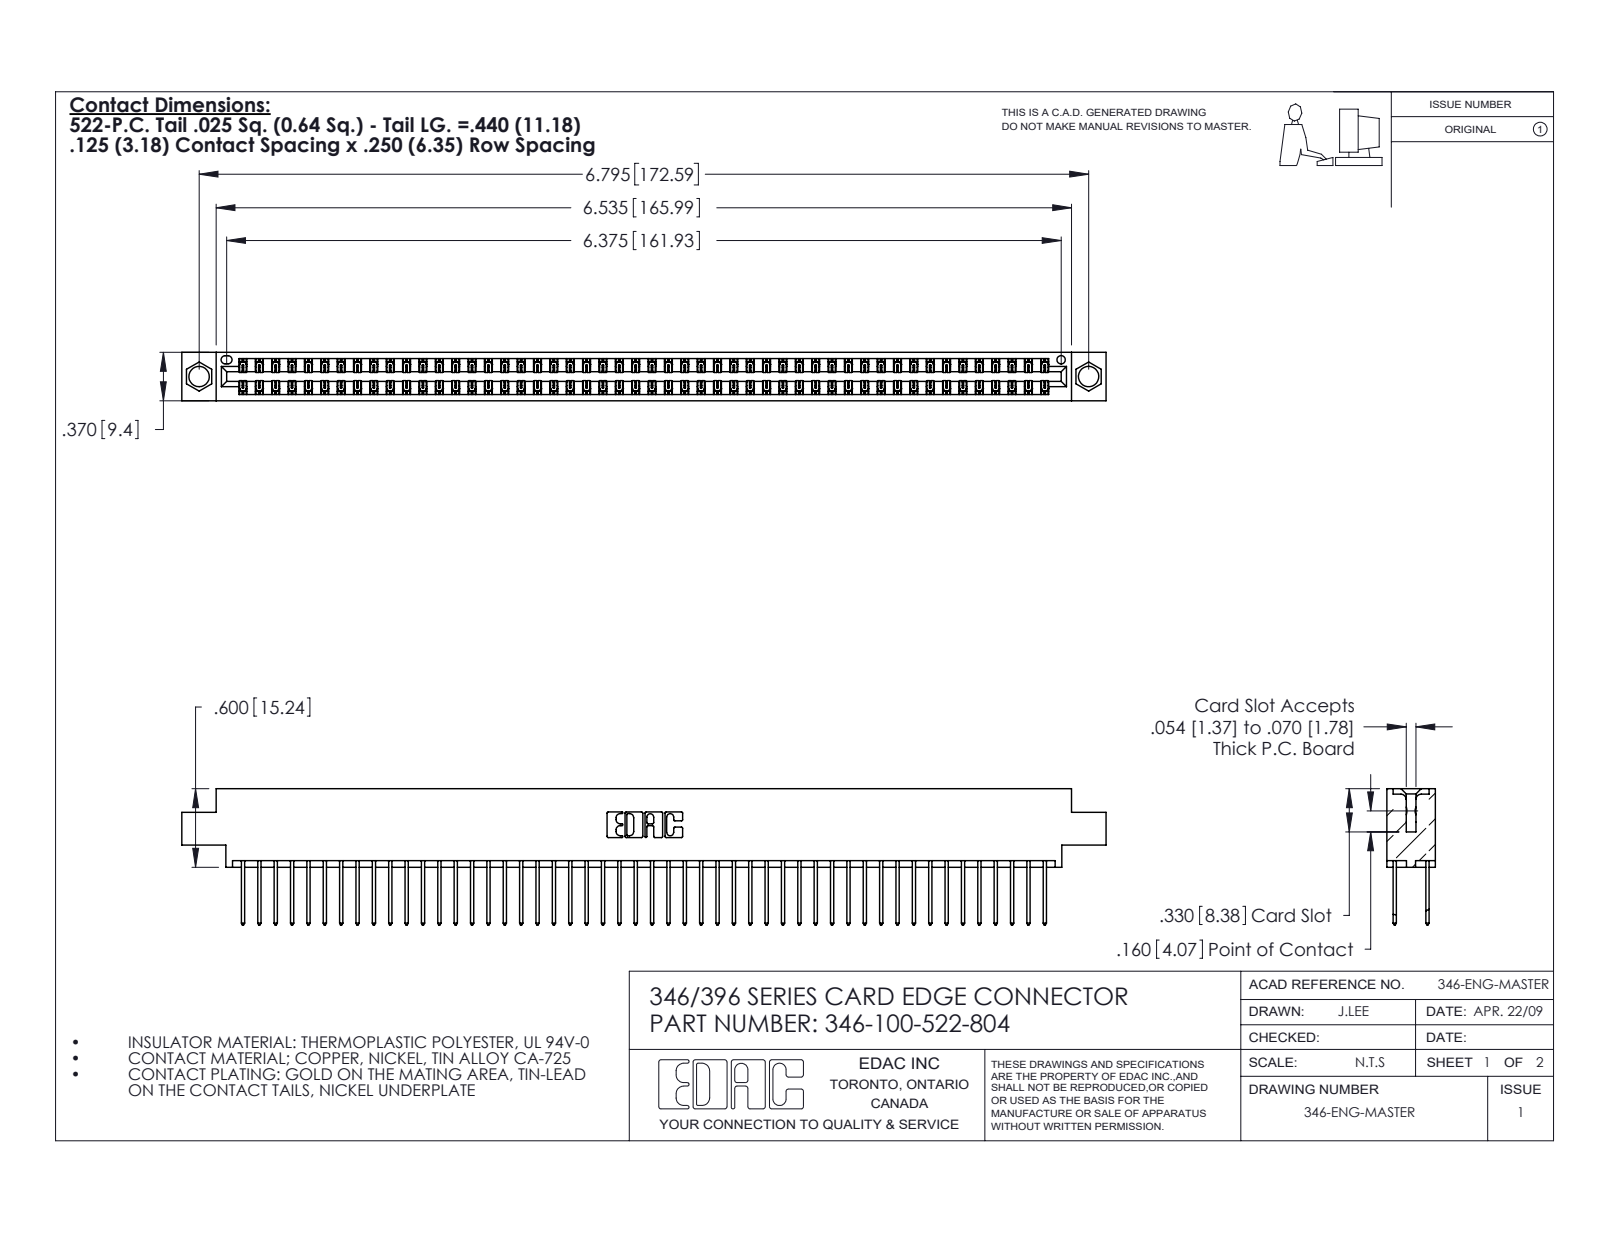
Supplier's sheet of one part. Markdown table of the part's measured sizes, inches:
| quantity | value |
| --- | --- |
| part name | 346-100-522-804; 346 Part_0.170 Offset - 0.156 Dia-TH; 345-292-001_345-293-122 |
| STEP written by | SolidWorks 2020 (CONFIG_CONTROL_DESIGN) |
| units | inches |
| bodies | 101 solids, 5340 faces (3594 planar, 1746 cylindrical, 0 other) |
| overall size | 7.06 × 1.04 × 0.37 |
| volume | 1.071 in³ |
| surface area | 39.46 in² |
| round holes (diameter × count) | 0.156 × 2, 0.064 × 1 |
| partial cylindrical surfaces (radius × count) | 0.006 × 150, 0.01 × 100, 0.01 × 22, 0.007 × 6, 0.031 × 6, 0.026 × 3, 0.014 × 2, 0.022 × 2 |
| main face-to-face distances | 0.048, 0.322, 0.25, 0.37, 0.072, 0.298, 0.025, 0.275, 0.222, 0.148 |
| hole center spacings | 0.246, 6.586, 6.795 |
